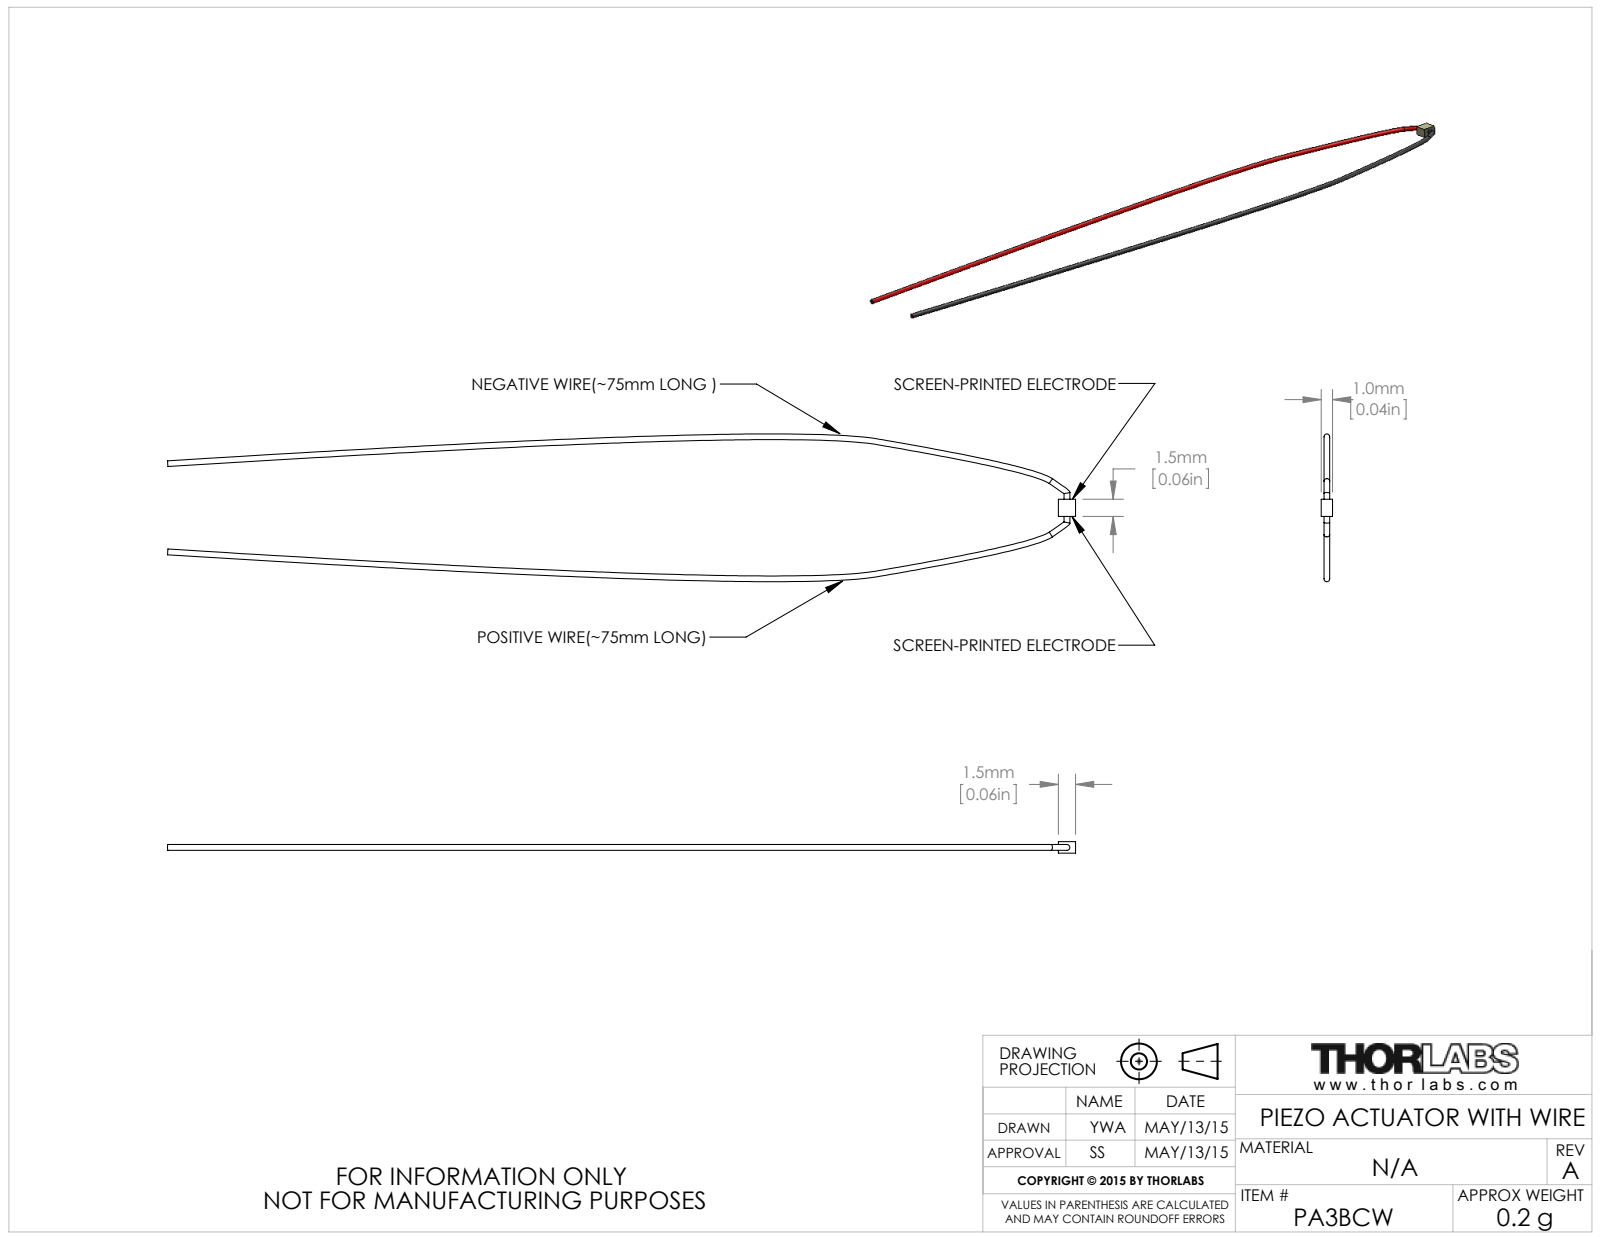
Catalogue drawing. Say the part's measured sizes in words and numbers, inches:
The part is named "CTN002636". Its 3-D file was written by "SolidWorks 2014 (AUTOMOTIVE_DESIGN)". It is 1 solid with 20 faces: 8 planar, 4 cylindrical and 8 other. Overall it measures 3.121 by 0.508 by 0.039 inches. Its volume is 0.002 cubic inches and its surface area 0.406 square inches. Round bosses or shafts: 1 of diameter 0.02. The main face-to-face distances are 0.059, 0.039.
